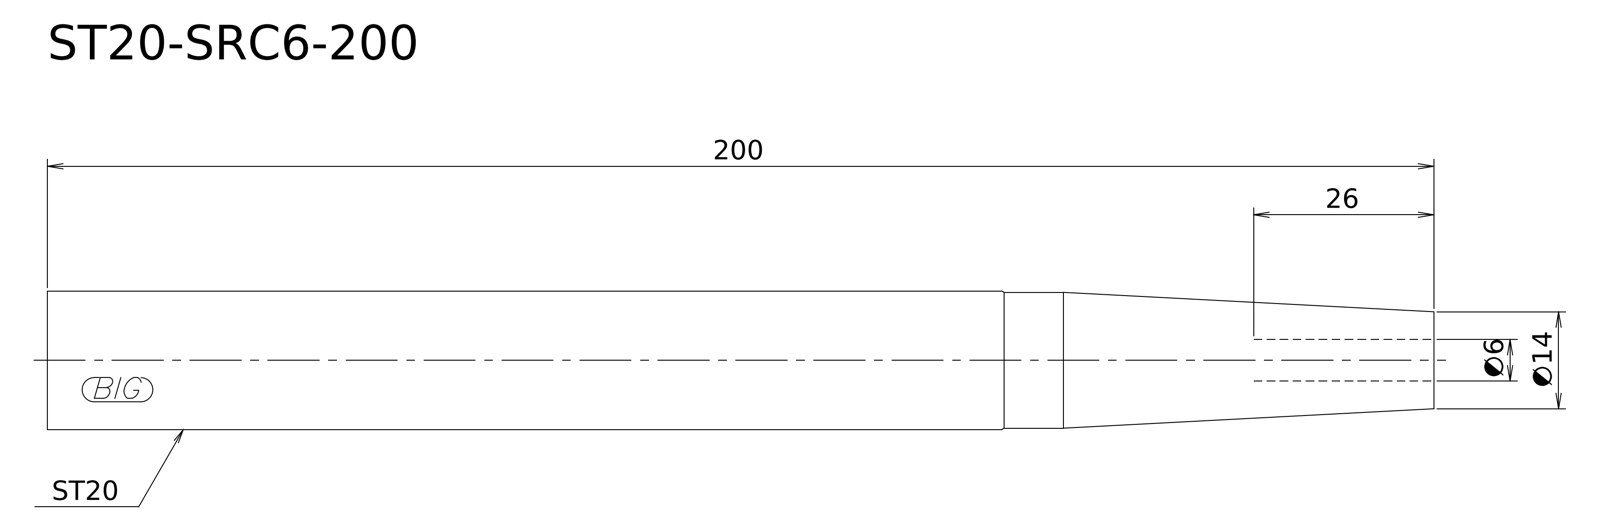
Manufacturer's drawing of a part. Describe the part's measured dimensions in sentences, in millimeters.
Its 3-D file was written by "Kubotek KeyCreator V8.5.1 (14335) (CONFIG_CONTROL_DESIGN)". It is 1 solid with 6 faces: 2 planar, 2 cylindrical and 2 other. Overall it measures 200 by 20 by 20 millimeters. Its volume is 57 891 cubic millimeters and its surface area 12 494 square millimeters. Round bosses or shafts: 1 of diameter 20, 1 of diameter 19.6. The main face-to-face distances are 200.
